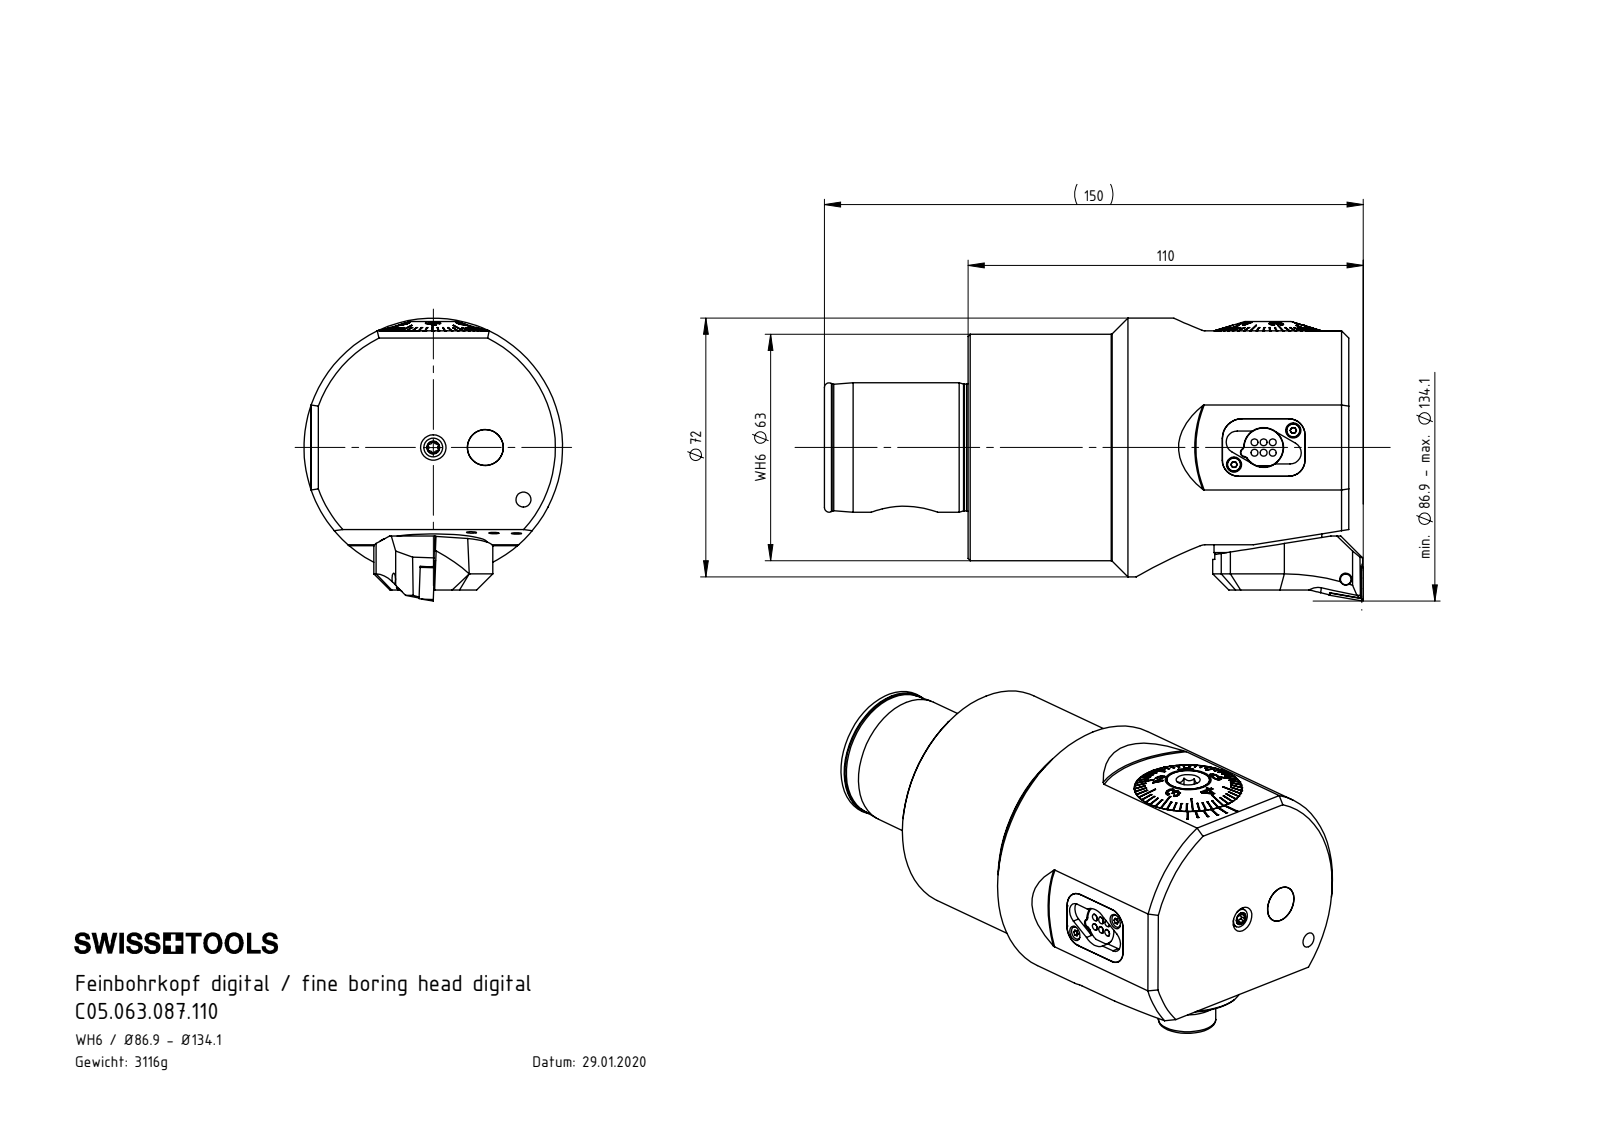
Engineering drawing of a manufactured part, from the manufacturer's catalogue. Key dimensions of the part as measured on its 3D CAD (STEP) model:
Part name (STEP PRODUCT): PEF-DA3.010.032_A_F72; F72-BG1.DA3.030_A; F72-BG2.014.020_B_mit Gewinde; A55-BG3.011.033_A_gekrzt (+8 more)
STEP written by: SolidWorks 2017 (CONFIG_CONTROL_DESIGN)
Units: millimetres
Bodies: 31 solids, 1001 faces (466 planar, 218 cylindrical, 317 other)
Overall size (bounding box): 146 × 75.66 × 72
Volume: 392 040 mm³ · Surface area: 67 692 mm²
Round holes (diameter × count): ⌀4.2 ×5, ⌀2.5 ×3, ⌀8.5 ×3, ⌀1.6 ×2, ⌀2.2 ×2, ⌀3.3 ×2, ⌀12 ×2, ⌀13 ×2, ⌀5 ×1, ⌀8 ×1, ⌀9.5 ×1, ⌀10 ×1
Round bosses / shafts (diameter × count): ⌀1.9 ×6, ⌀10 ×2, ⌀3.8 ×2, ⌀2 ×2, ⌀72 ×1, ⌀63 ×1, ⌀36 ×1, ⌀35.3 ×1
Partial cylindrical surfaces — rounded edges, fillets, slot ends (radius × count): R0.34 ×6, R0.59 ×6, R1.1 ×6, R1.2 ×6, R2 ×6, R2.5 ×6, R3.2 ×3, R4.4 ×3
Main face-to-face distances: 106, 53.01, 40, 146, 2.6, 62.11, 59.51, 6.5, 1.2, 2.8
Hole centre spacings: 9.52, 1.21, 8.49, 10.59, 14.5, 17.97, 19.04, 19.81
